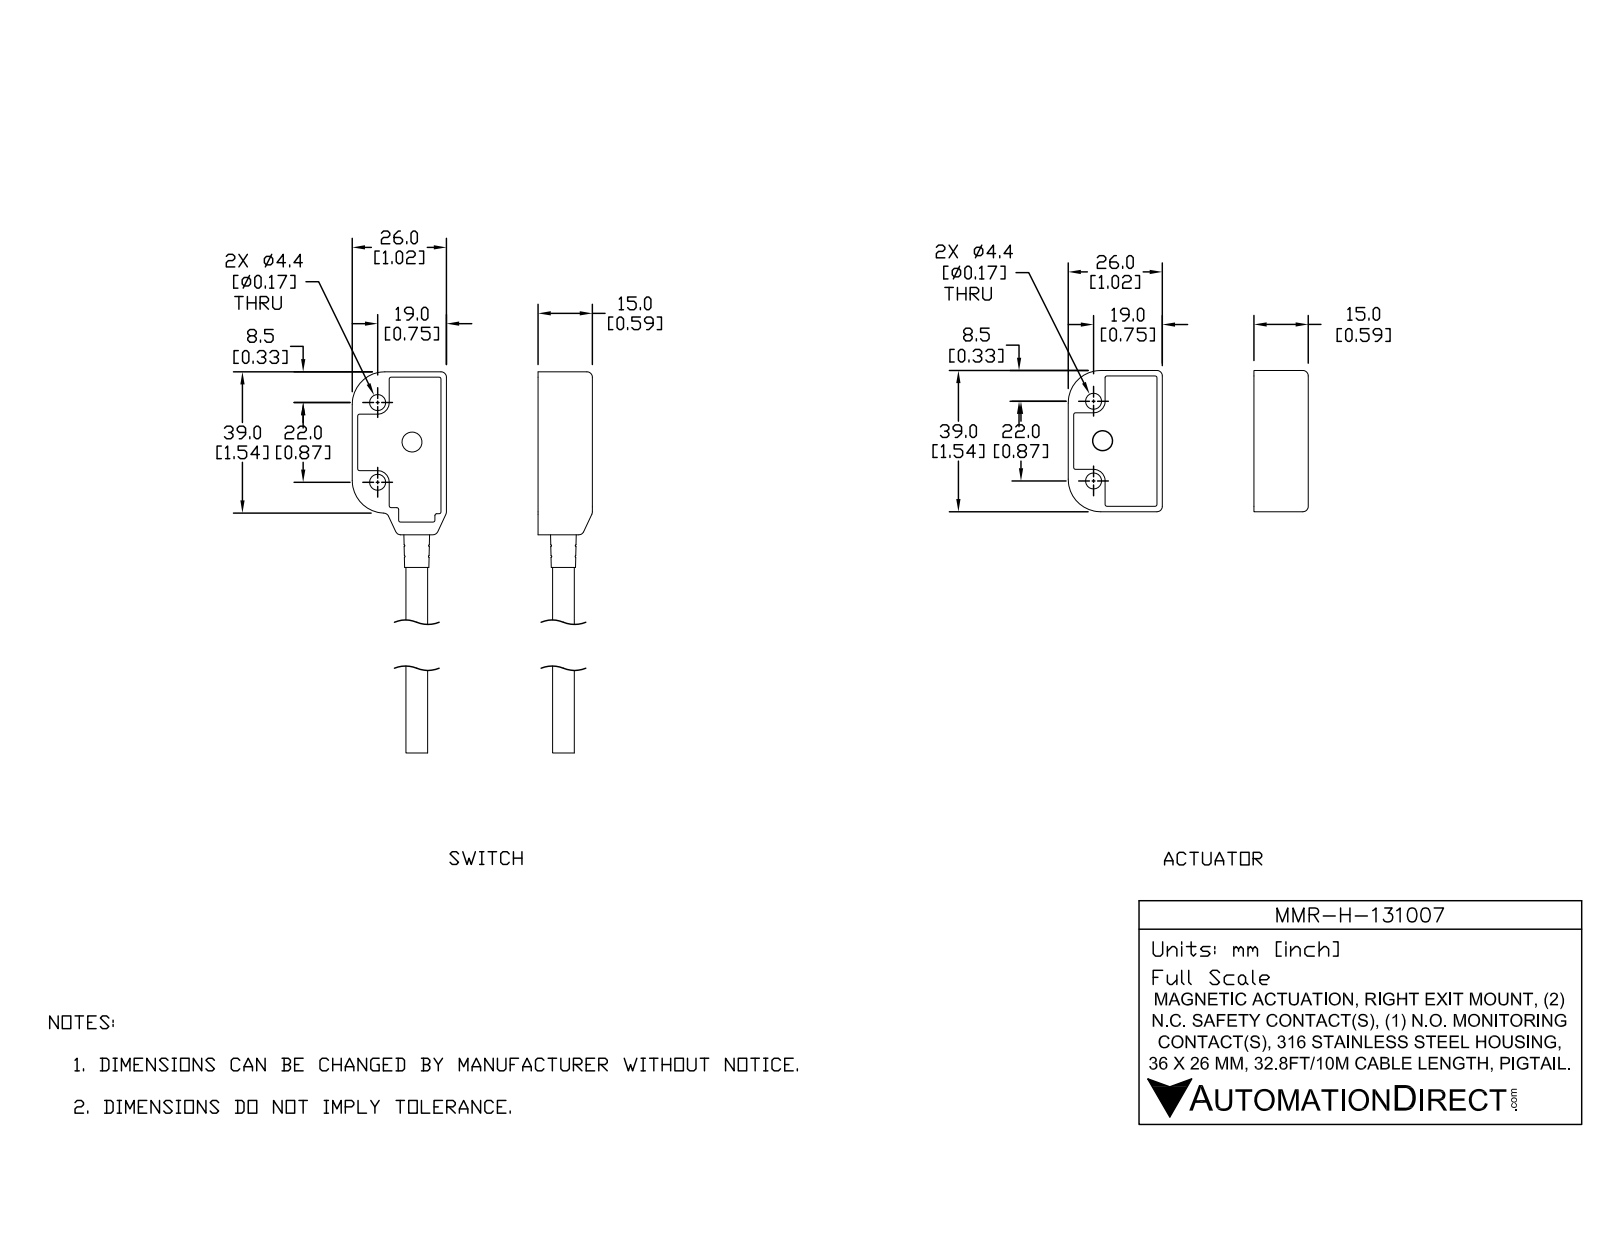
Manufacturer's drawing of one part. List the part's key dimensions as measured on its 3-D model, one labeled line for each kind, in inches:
Part name (STEP PRODUCT): MMR-H-131007_1; MMR-H-131007; MMR-H-131007_2
STEP written by: SolidWorks 2017 (AUTOMOTIVE_DESIGN)
Units: inches
Bodies: 7 solids, 584 faces (173 planar, 224 cylindrical, 187 other)
Overall size (bounding box): 7.803 × 2.087 × 0.591
Volume: 1.232 in³ · Surface area: 30.25 in²
Round holes (diameter × count): ⌀0.173 ×4, ⌀0.197 ×2, ⌀0.232 ×1, ⌀0.283 ×1
Round bosses / shafts (diameter × count): ⌀0.079 ×2, ⌀0.339 ×1, ⌀0.299 ×1, ⌀0.28 ×1, ⌀0.236 ×1, ⌀0.118 ×1
Partial cylindrical surfaces — rounded edges, fillets, slot ends (radius × count): R0.02 ×82, R0.012 ×26, R0.059 ×15, R0.008 ×8, R0.157 ×6, R0.126 ×4, R0.13 ×4, R0.181 ×4
Main face-to-face distances: 0.059, 0.575, 0.516, 0.461, 0.098, 0.52, 0.055, 0.591, 0.531, 0.965
Hole centre spacings: 0.866, 1.535, 1.763, 0.44, 0.448, 0.569, 0.575, 1.063
